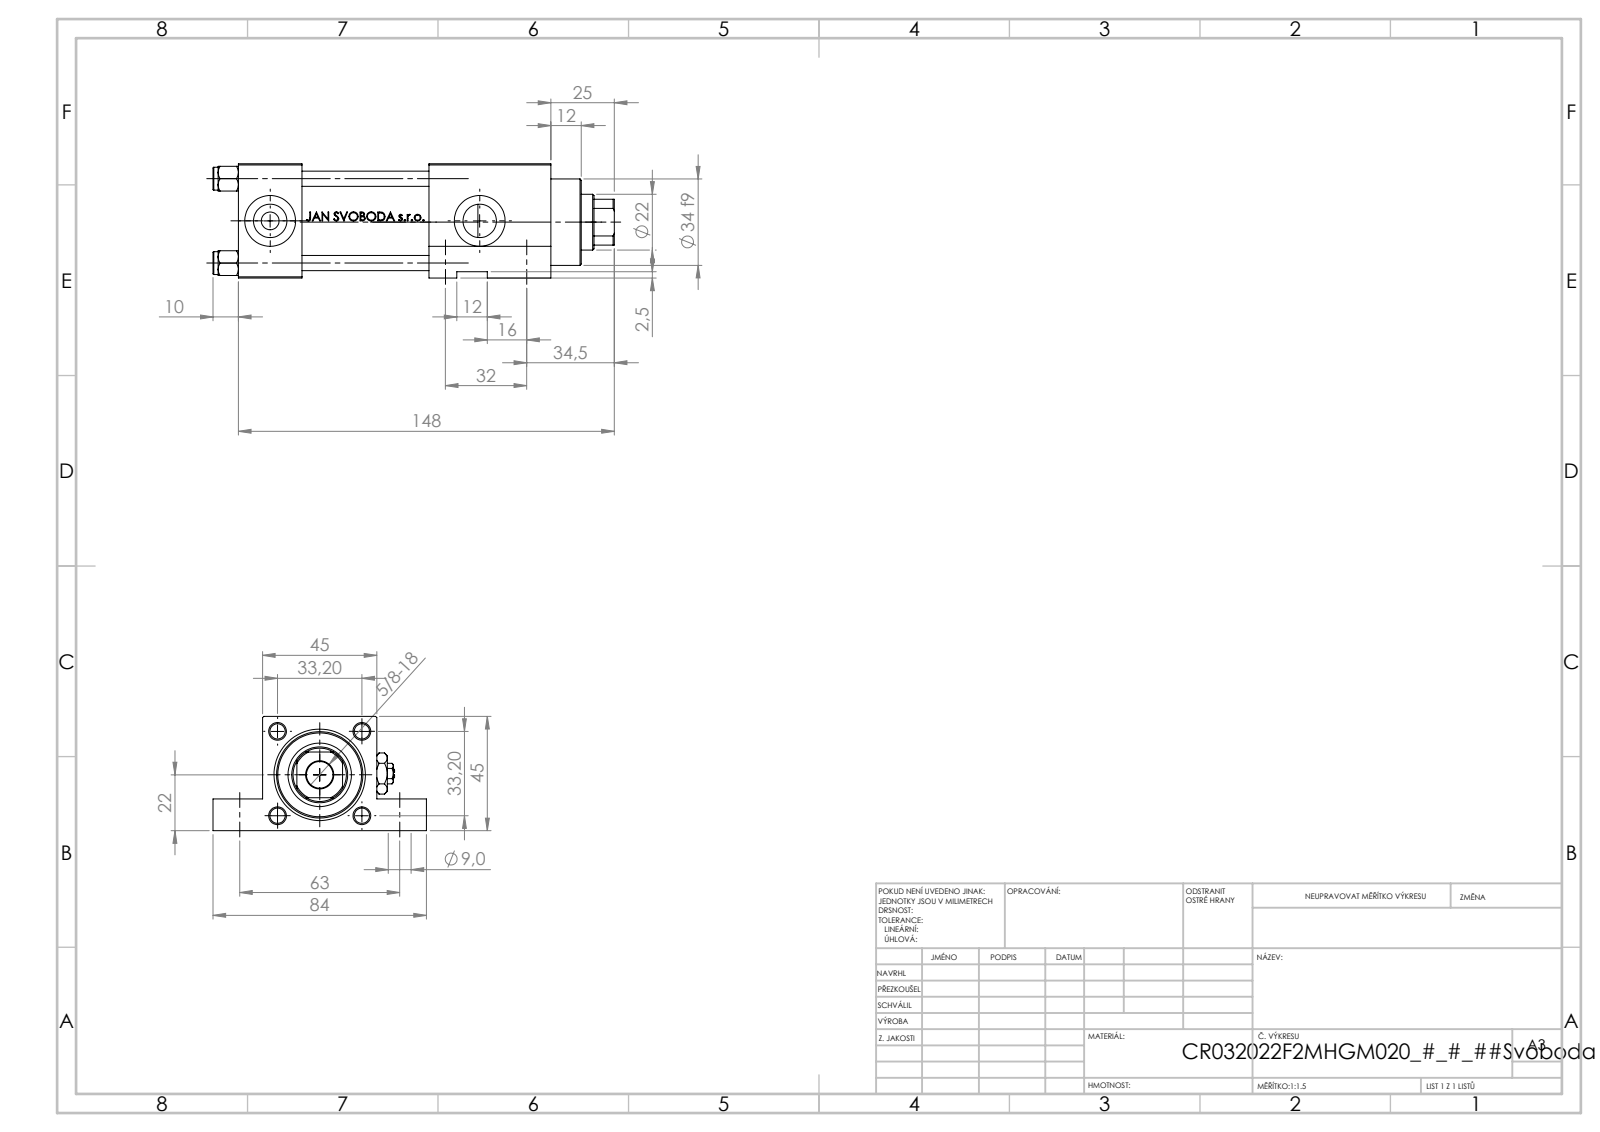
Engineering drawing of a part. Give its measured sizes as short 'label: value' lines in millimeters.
name: V215CR_F_TYCINKA; V215_VC_A; NUT_M5_F; V215CR_F_Body (+2 more)
written by: SolidWorks 2019 (CONFIG_CONTROL_DESIGN)
unit: mm
bodies: 12 solids, 1150 faces (458 planar, 130 cylindrical, 562 other)
size: 158 × 84 × 45
volume: 227 061 mm³; area: 77 944 mm²
holes: 4× ⌀6, 4× ⌀9, 2× ⌀7, 2× ⌀13.16, 2× ⌀20, 1× ⌀10.5, 1× ⌀13, 1× ⌀22, 1× ⌀24, 1× ⌀25, 1× ⌀32, 1× ⌀33
bosses: 4× ⌀9, 1× ⌀38, 1× ⌀34
rounds: 1× R10.5
face distances: 45, 25, 50, 98, 123, 75, 12.5, 32.5, 48, 10
hole spacings: 33.2, 23.13, 23.83, 32, 46.95, 63, 70.66, 82.5
